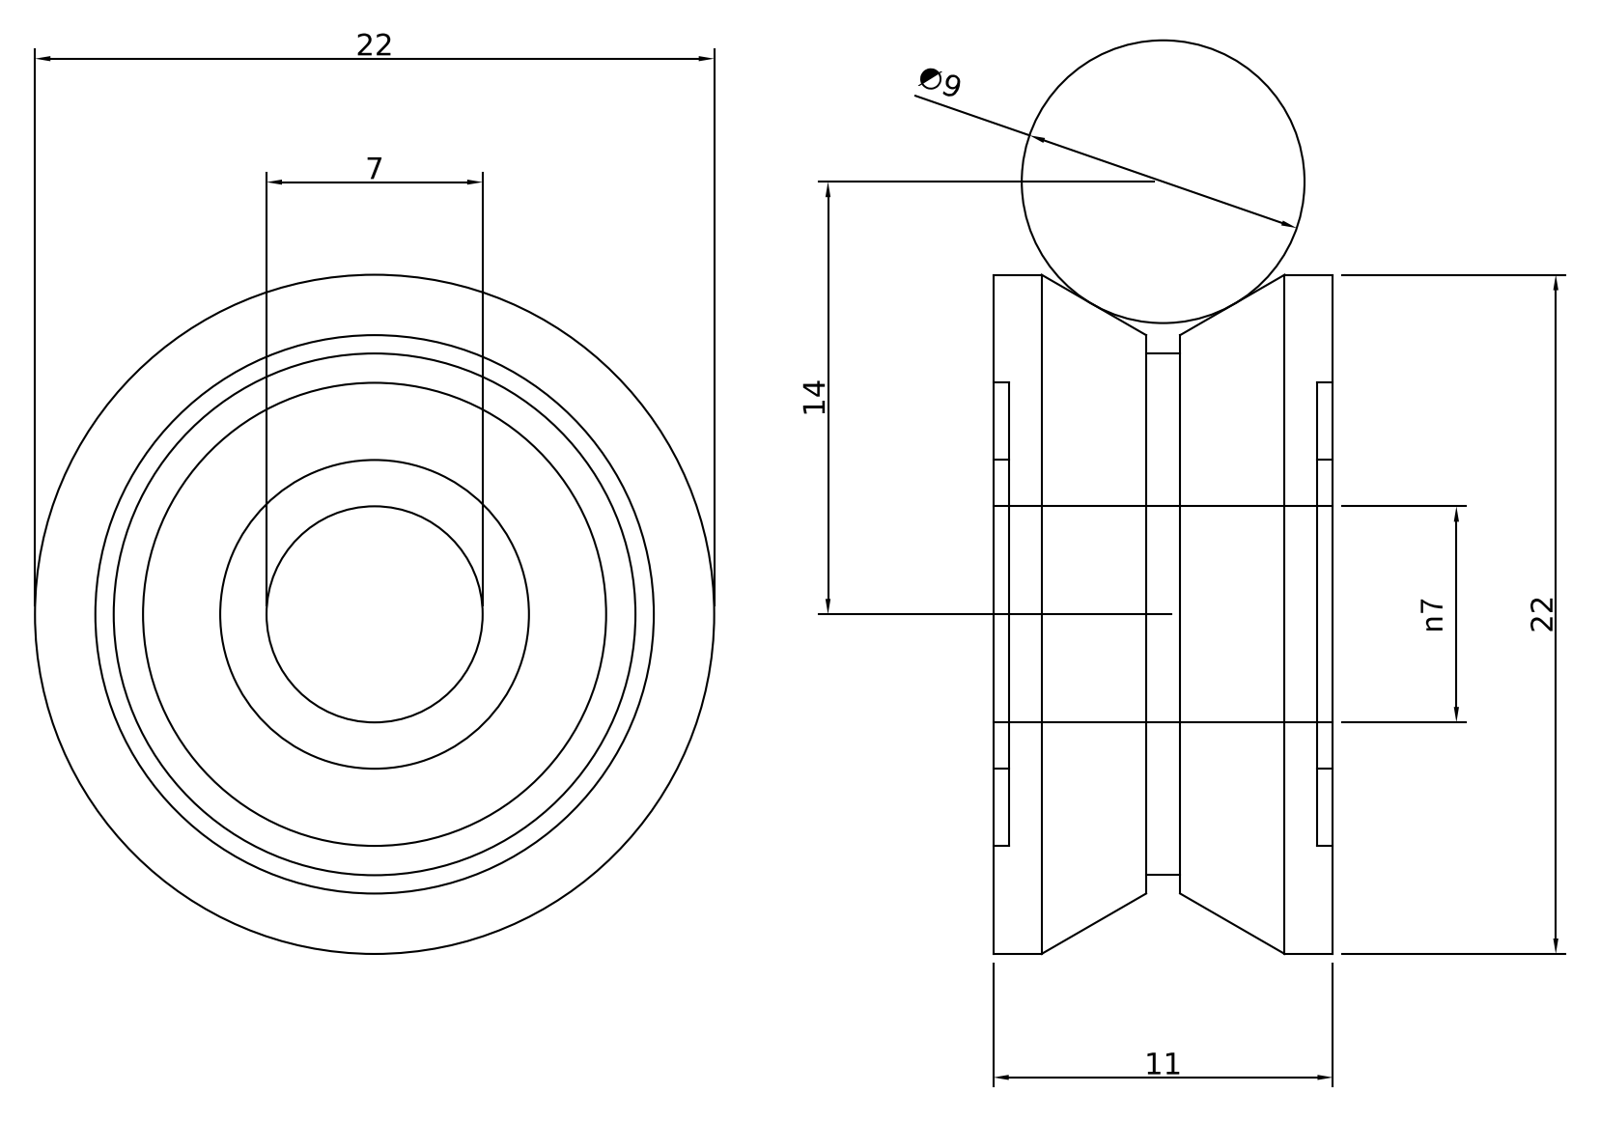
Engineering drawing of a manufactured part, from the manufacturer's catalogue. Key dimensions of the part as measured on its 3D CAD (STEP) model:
Part name (STEP PRODUCT): 80RT00013R-A
STEP written by: Autodesk Inventor 2022 (AUTOMOTIVE_DESIGN)
Units: millimetres
Bodies: 1 solid, 18 faces (8 planar, 8 cylindrical, 2 other)
Overall size (bounding box): 22 × 22 × 11
Volume: 3 058 mm³ · Surface area: 1 836 mm²
Round holes (diameter × count): ⌀7 ×1, ⌀15 ×1
Round bosses / shafts (diameter × count): ⌀22 ×1, ⌀16.9 ×1, ⌀10 ×1
Main face-to-face distances: 11, 0.5, 10.5, 10, 4.95, 6.05, 4.45, 5.55, 1.1
